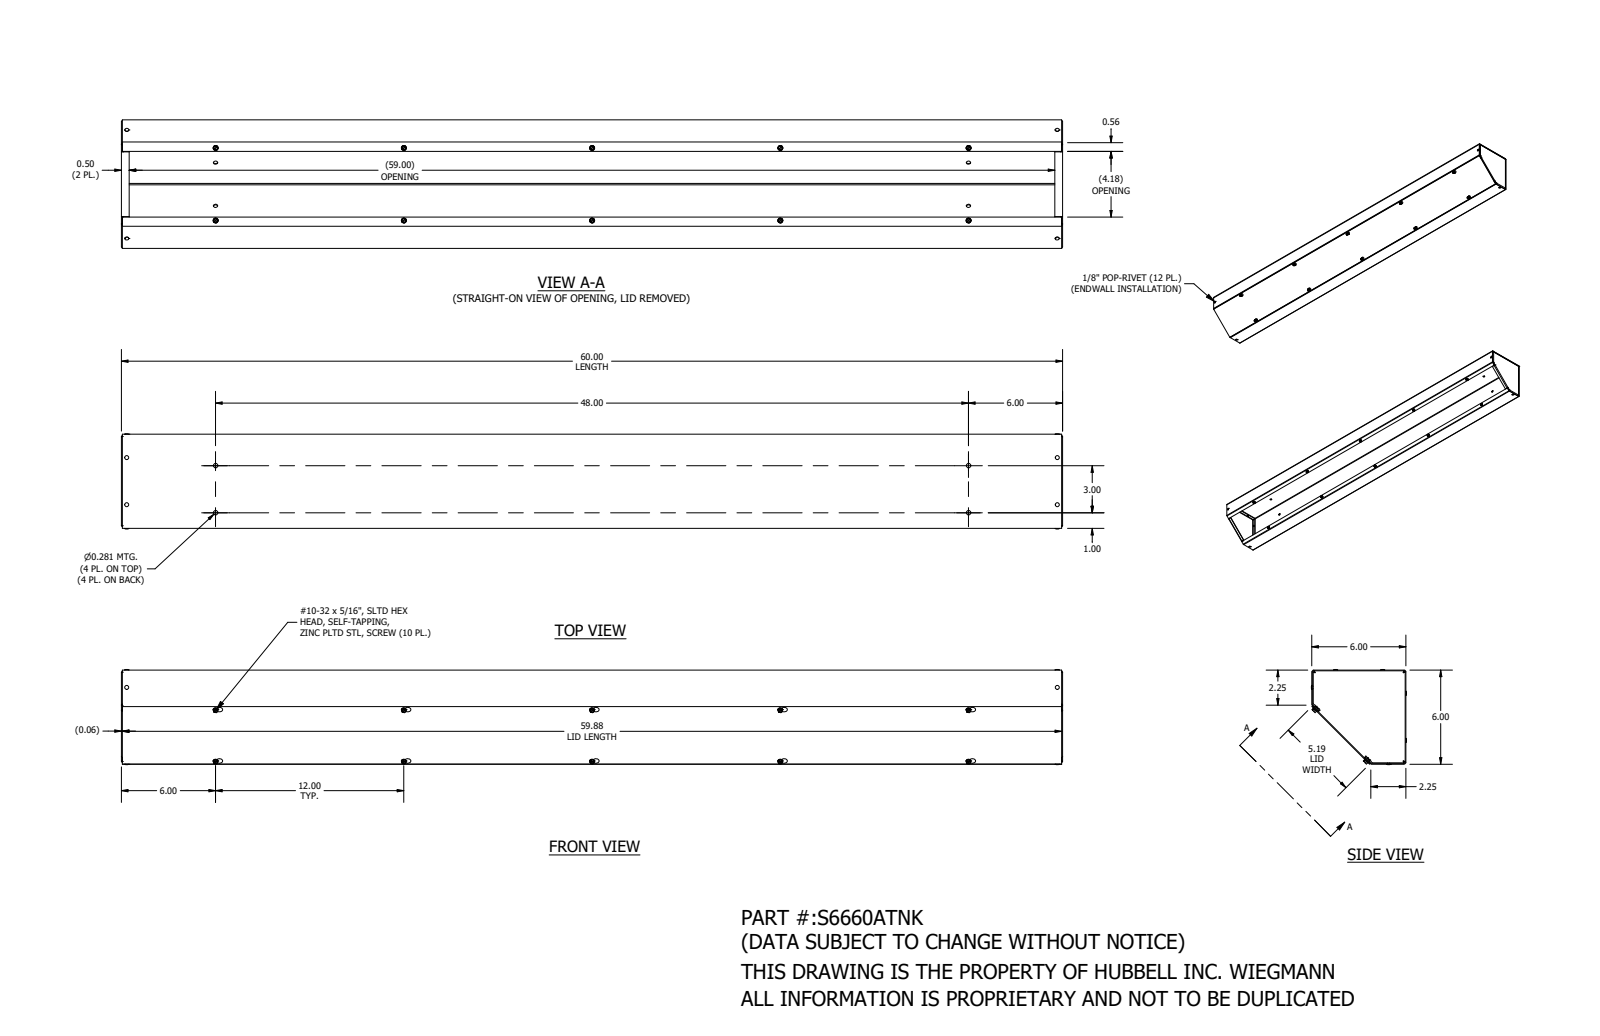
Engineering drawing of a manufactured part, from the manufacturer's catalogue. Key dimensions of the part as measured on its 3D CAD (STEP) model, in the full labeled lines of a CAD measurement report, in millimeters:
Part name (STEP PRODUCT): S6660ATNK
STEP written by: SolidWorks 2021 (AUTOMOTIVE_DESIGN)
Units: millimetres
Bodies: 26 solids, 1140 faces (410 planar, 248 cylindrical, 482 other)
Overall size (bounding box): 1524 × 154.4 × 154.4
Volume: 1 278 000 mm³ · Surface area: 1 845 000 mm²
Round holes (diameter × count): ⌀3.3 ×12, ⌀4.3 ×10, ⌀10.3 ×10, ⌀7.1 ×8
Round bosses / shafts (diameter × count): ⌀6.7 ×12, ⌀3.2 ×12, ⌀8 ×10, ⌀4.6 ×10
Partial cylindrical surfaces — rounded edges, fillets, slot ends (radius × count): R1.6 ×24, R1.6 ×10, R2.8 ×10, R3 ×9, R3 ×6, R1.6 ×5
Main face-to-face distances: 1.4, 151, 152.4, 149.6, 1.2, 2.6, 1.4, 1524, 1522.6, 1522.6
Hole centre spacings: 304.8, 609.6, 620.8, 6.4, 76.2, 144.3, 298.5, 311.2
